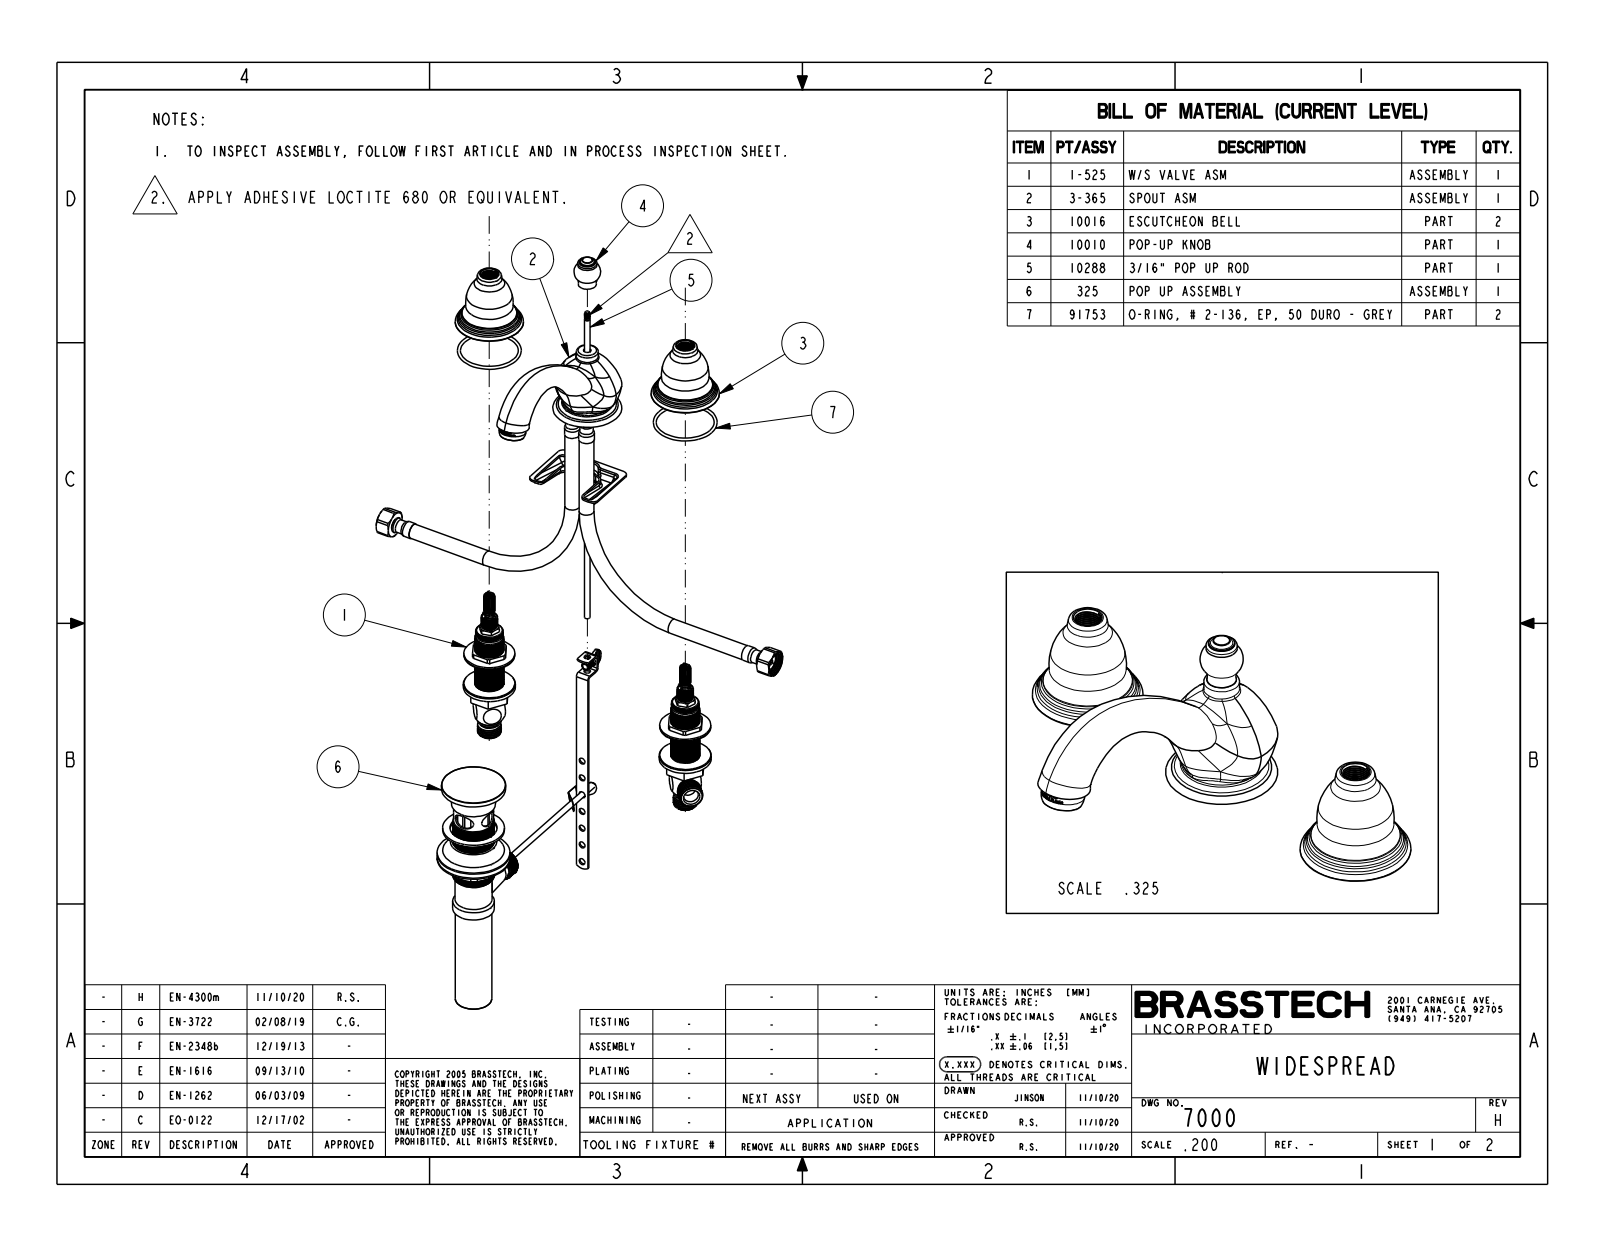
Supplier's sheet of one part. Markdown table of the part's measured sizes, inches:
| quantity | value |
| --- | --- |
| part name | 7000 |
| STEP written by | CREO PARAMETRIC BY PTC INC, 2018400 (CONFIG_CONTROL_DESIGN) |
| units | inches |
| bodies | 3 solids, 228 faces (48 planar, 45 cylindrical, 135 other) |
| overall size | 10.34 × 6.442 × 3.415 |
| volume | 18.67 in³ |
| surface area | 72.65 in² |
| round holes (diameter × count) | 0.792 × 1 |
| round bosses / shafts (diameter × count) | 2.34 × 2, 1.72 × 1, 0.925 × 1, 0.78 × 1, 0.755 × 1, 0.715 × 1, 0.661 × 1, 0.655 × 1 |
| main face-to-face distances | 2.008, 0.363, 0.356, 0.235, 0.227, 0.128, 3.415, 1.407, 0.013, 0.222 |
